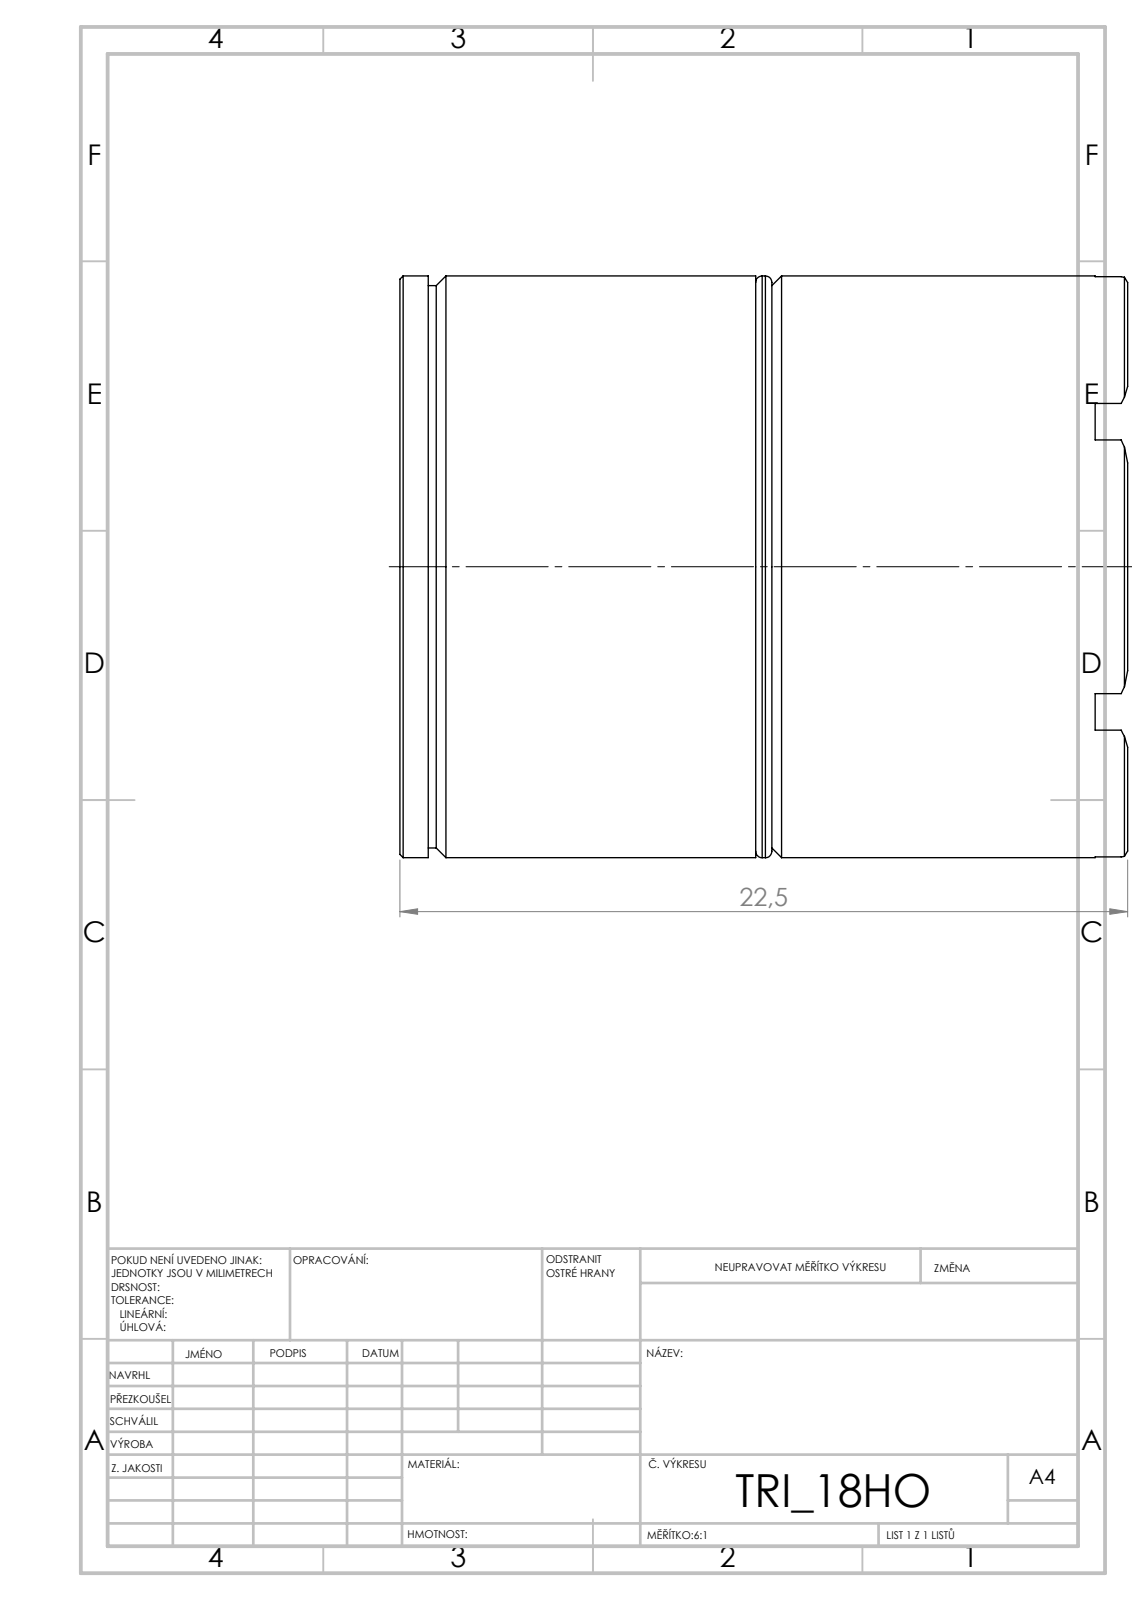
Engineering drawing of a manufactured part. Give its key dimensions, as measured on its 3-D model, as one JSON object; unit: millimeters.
{"step_written_by": "SolidWorks 2019 (CONFIG_CONTROL_DESIGN)", "units": "millimeters", "bodies": {"solids": 2, "faces": 53, "planar": 24, "cylindrical": 12, "other": 17}, "overall_size": [22.5, 18, 18], "volume_mm3": 5607, "surface_area_mm2": 2381, "round_bosses_or_shafts": [[18, 1], [17.4, 1]], "face_to_face_distances": [11, 11.5, 0.5, 10, 10.5, 21.5, 16.2, 20.63, 10.63, 10.13]}
